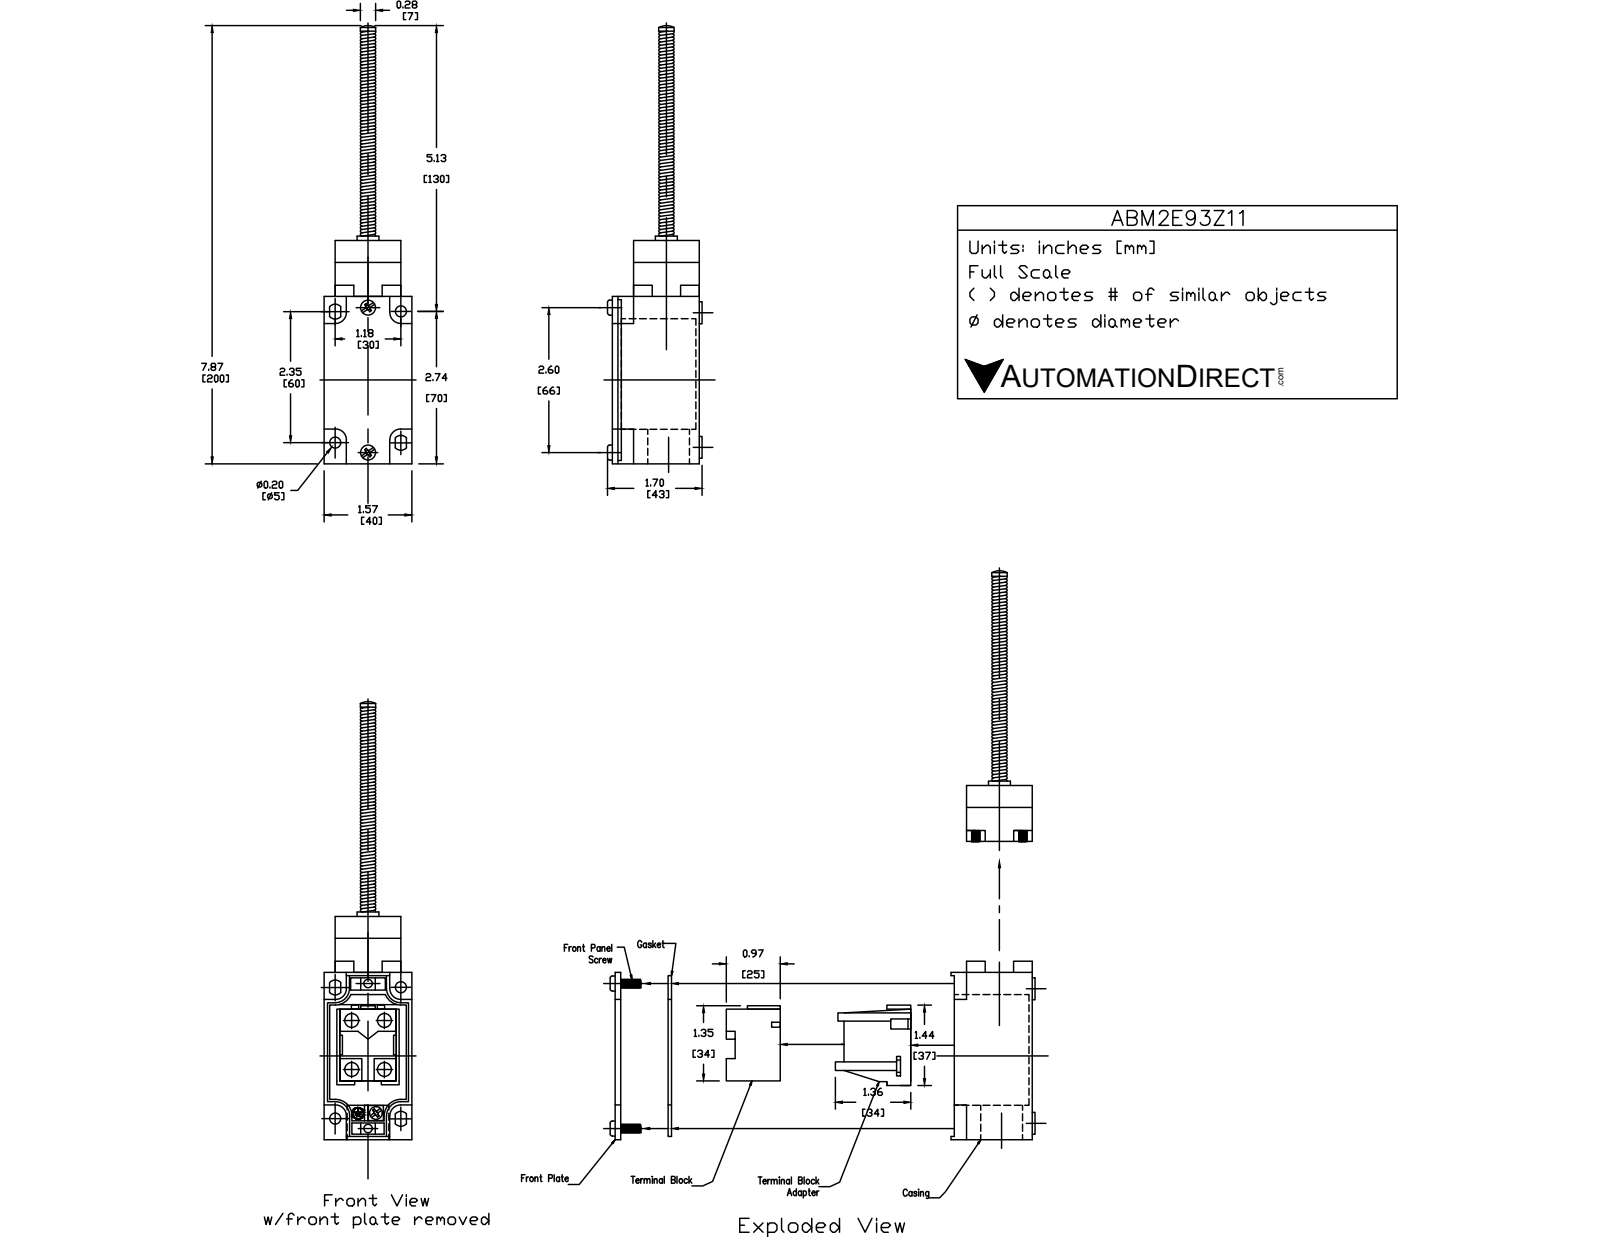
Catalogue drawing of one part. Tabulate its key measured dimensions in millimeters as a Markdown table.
| quantity | value |
| --- | --- |
| part name | ABM2E93Z11 |
| STEP written by | SolidWorks 2017 (AUTOMOTIVE_DESIGN) |
| units | millimeters |
| bodies | 3 solids, 196 faces (78 planar, 84 cylindrical, 34 other) |
| overall size | 198.3 × 43.3 × 40 |
| volume | 130 500 mm³ |
| surface area | 25 350 mm² |
| round holes (diameter × count) | 5.2 × 2, 17 × 1, 19 × 1, 20.5 × 1 |
| round bosses / shafts (diameter × count) | 7 × 7, 10 × 4, 19 × 1, 11.7 × 1, 6.8 × 1 |
| partial cylindrical surfaces (radius × count) | 1.5 × 16, 0.5 × 4, 0.6 × 4, 5 × 4, 3.3 × 2, 11.5 × 1, 12 × 1 |
| main face-to-face distances | 40, 39.5, 30, 5, 76.5, 9.5, 35, 77, 0.5, 81.5 |
| hole center spacings | 1, 67.1 |
